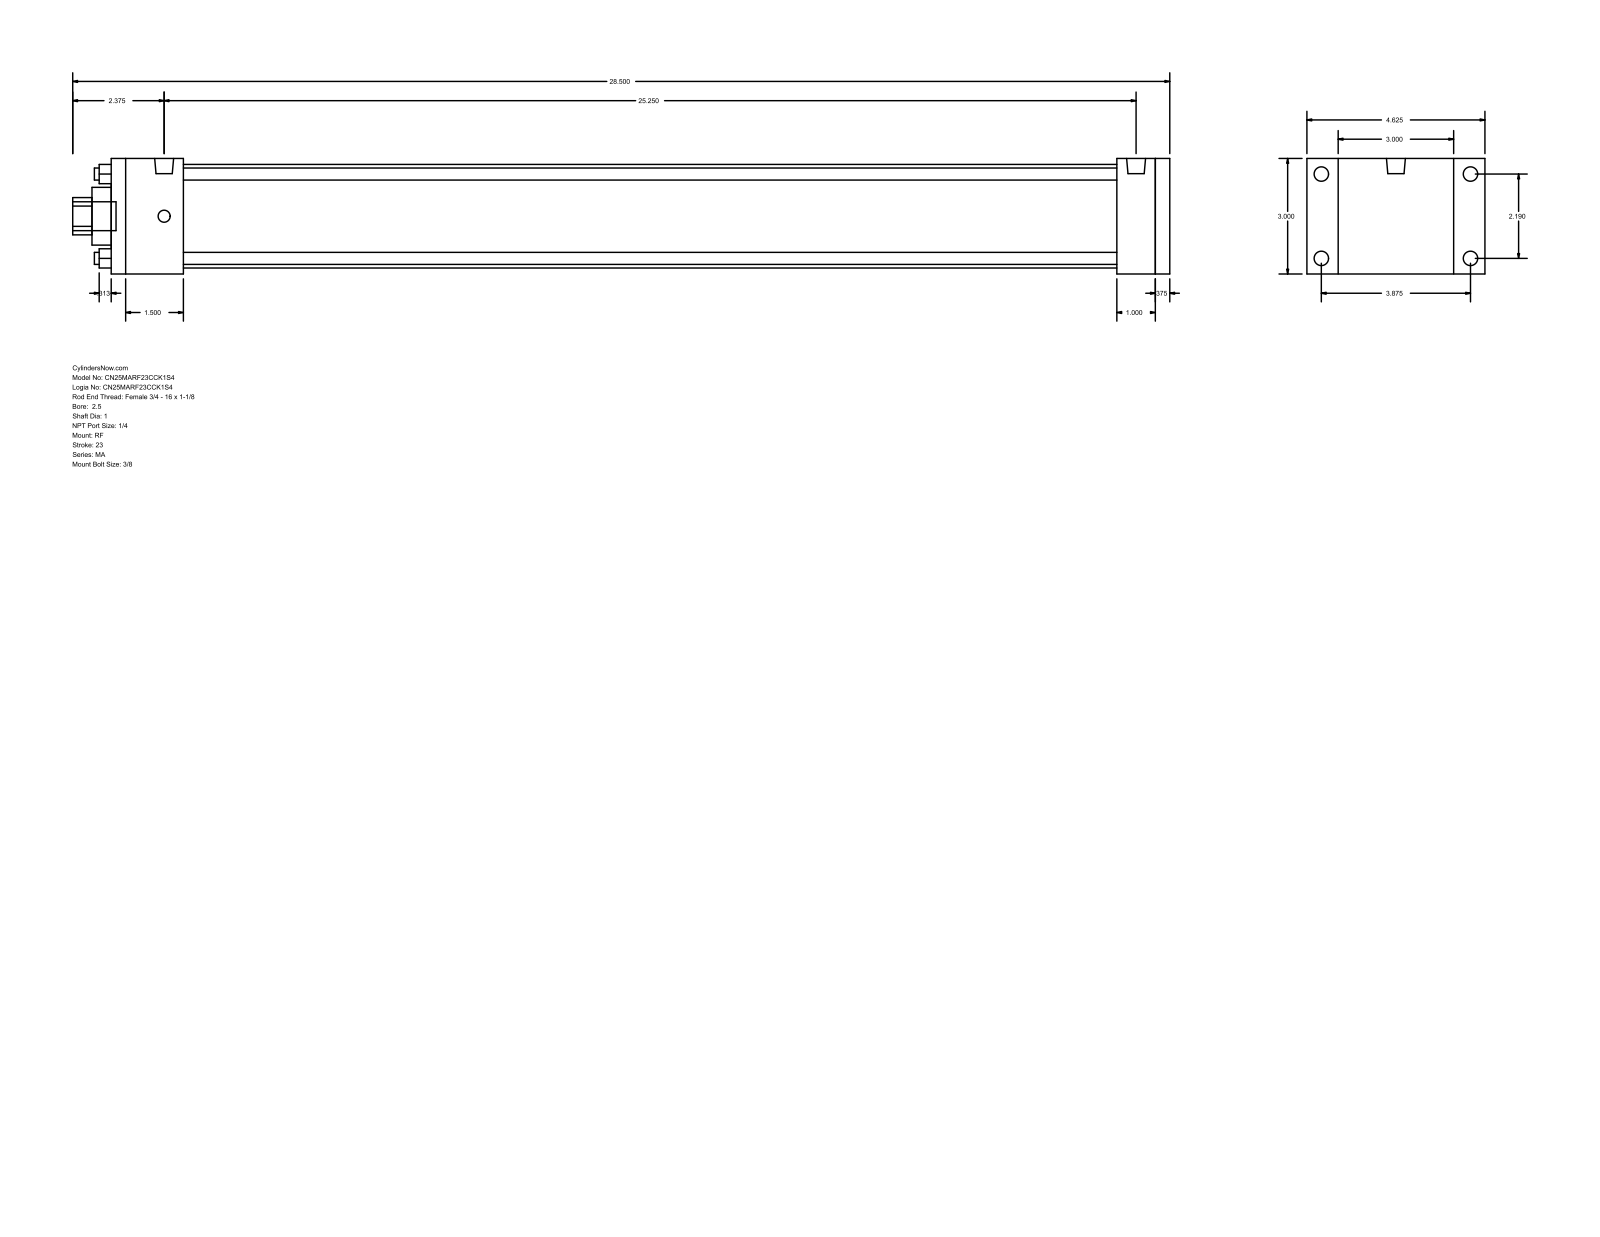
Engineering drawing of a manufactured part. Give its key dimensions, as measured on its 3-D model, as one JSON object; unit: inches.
{"part_name": "MA_RF__0250_1", "step_written_by": "GSSL Pune (CONFIG_CONTROL_DESIGN)", "units": "inches", "bodies": {"solids": 0, "faces": 92, "planar": 64, "cylindrical": 28, "other": 0}, "overall_size": [28.5, 4.625, 3], "round_holes": [[0.313, 4], [1, 1], [1.5, 1], [2.69, 1]], "round_bosses_or_shafts": [[0.375, 4], [0.313, 4], [0.492, 2], [0.75, 1]], "partial_cylinders_radius": [[0.484, 1]], "face_to_face_distances": [3, 27.5, 27.125, 0.375, 1, 1.875, 26.125, 24.25, 25.25, 25.625], "hole_center_spacings": [1.548, 2.19, 3.097]}
